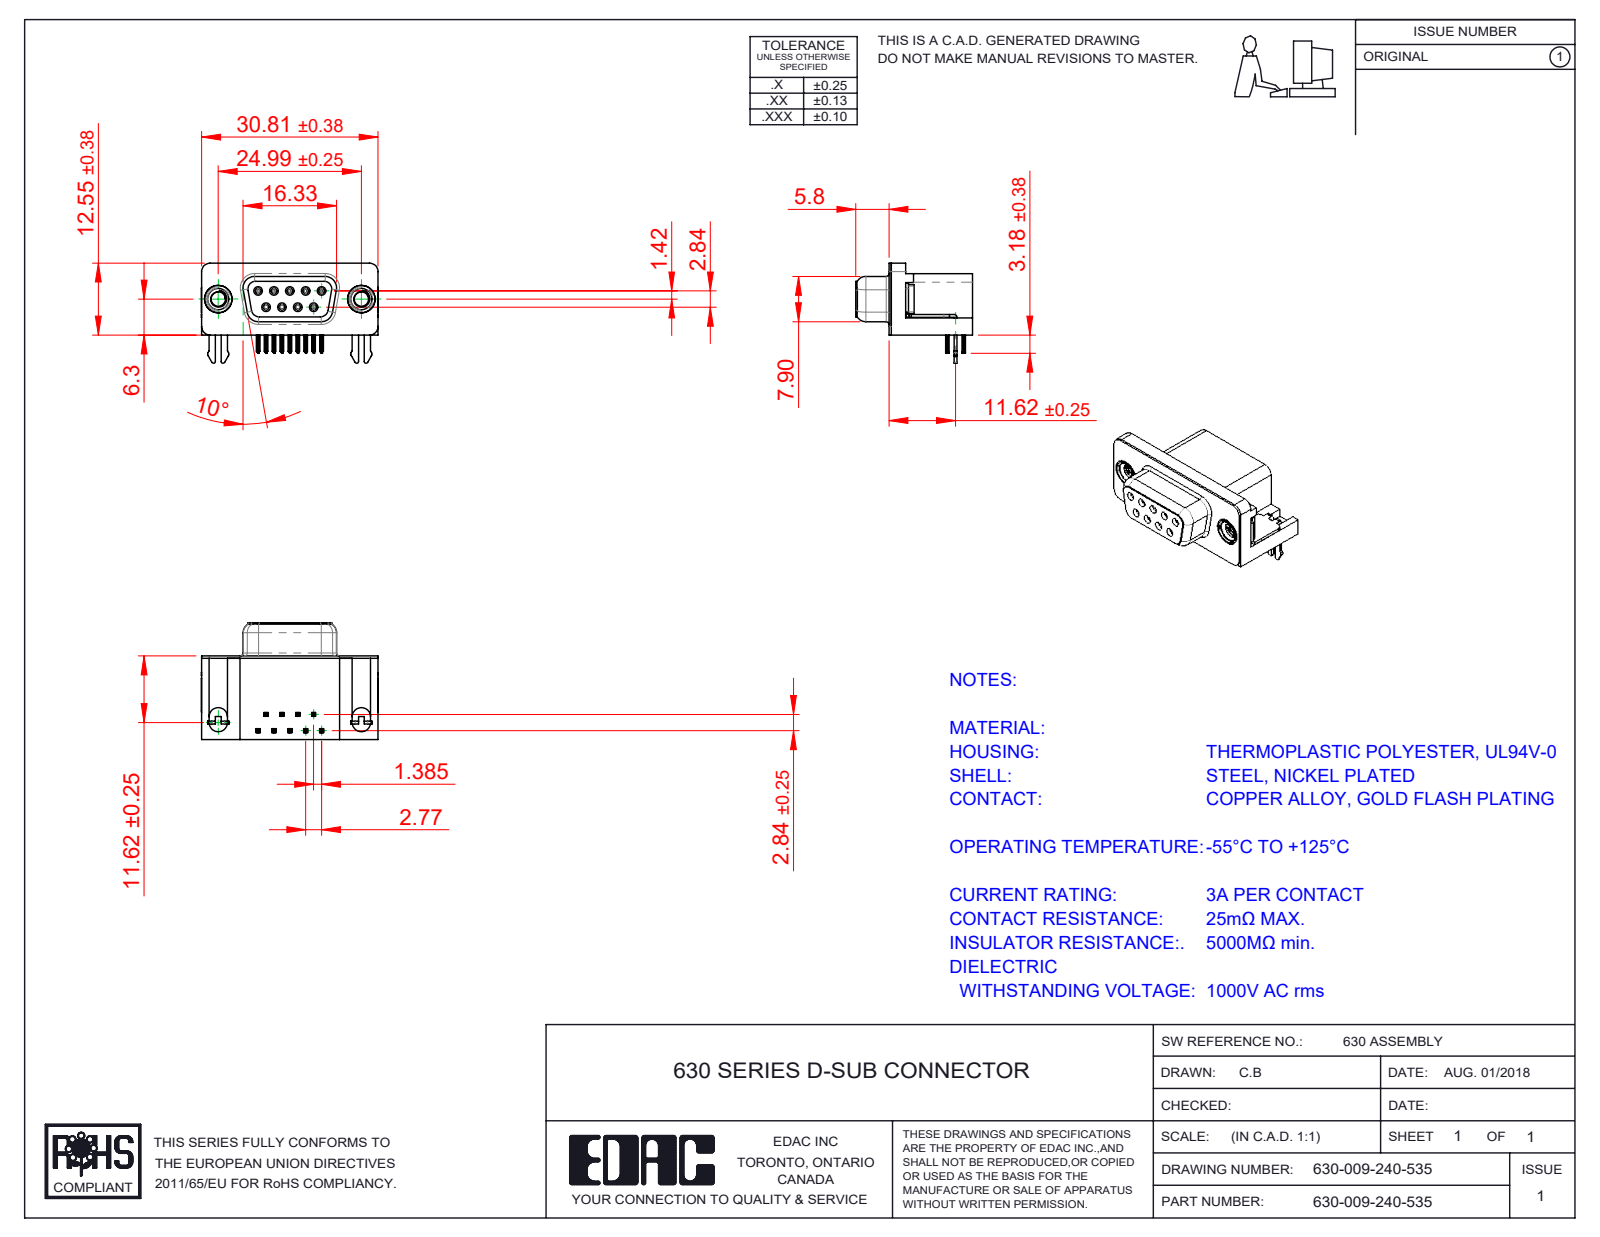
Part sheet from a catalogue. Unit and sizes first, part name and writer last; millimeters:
Units: millimetres
Overall size (bounding box): 30.89 × 20.4 × 17.48
Round holes (diameter × count): ⌀0.8 ×9, ⌀0.9 ×9, ⌀2.5 ×2, ⌀4 ×2, ⌀4.8 ×2, ⌀5 ×2
Round bosses / shafts (diameter × count): ⌀1.2 ×9, ⌀4.9 ×2, ⌀4.75 ×2, ⌀3.9 ×2
Partial cylindrical surfaces — rounded edges, fillets, slot ends (radius × count): R0.1 ×72, R0.15 ×36, R0.35 ×18, R1 ×18, R0.5 ×10, R0.34 ×9, R0.25 ×8, R1.35 ×8
Main face-to-face distances: 0.4, 14.6, 14.2, 10.34, 0.5, 6.2, 2.9, 2.5, 11.7, 0.35
Hole centre spacings: 3.16, 2.77, 5.54, 5.03, 5.04, 8.31, 7.48, 7.49
Volume: 4 199 mm³ · Surface area: 5 457 mm²
Bodies: 15 solids, 1610 faces (714 planar, 428 cylindrical, 468 other)
Part name (STEP PRODUCT): 630 M3 Threaded Rivet; 630 Contact Bottom; 630 Contact Top; 630-009-240-535 (+3 more)
STEP written by: SolidWorks 2020 (CONFIG_CONTROL_DESIGN)
